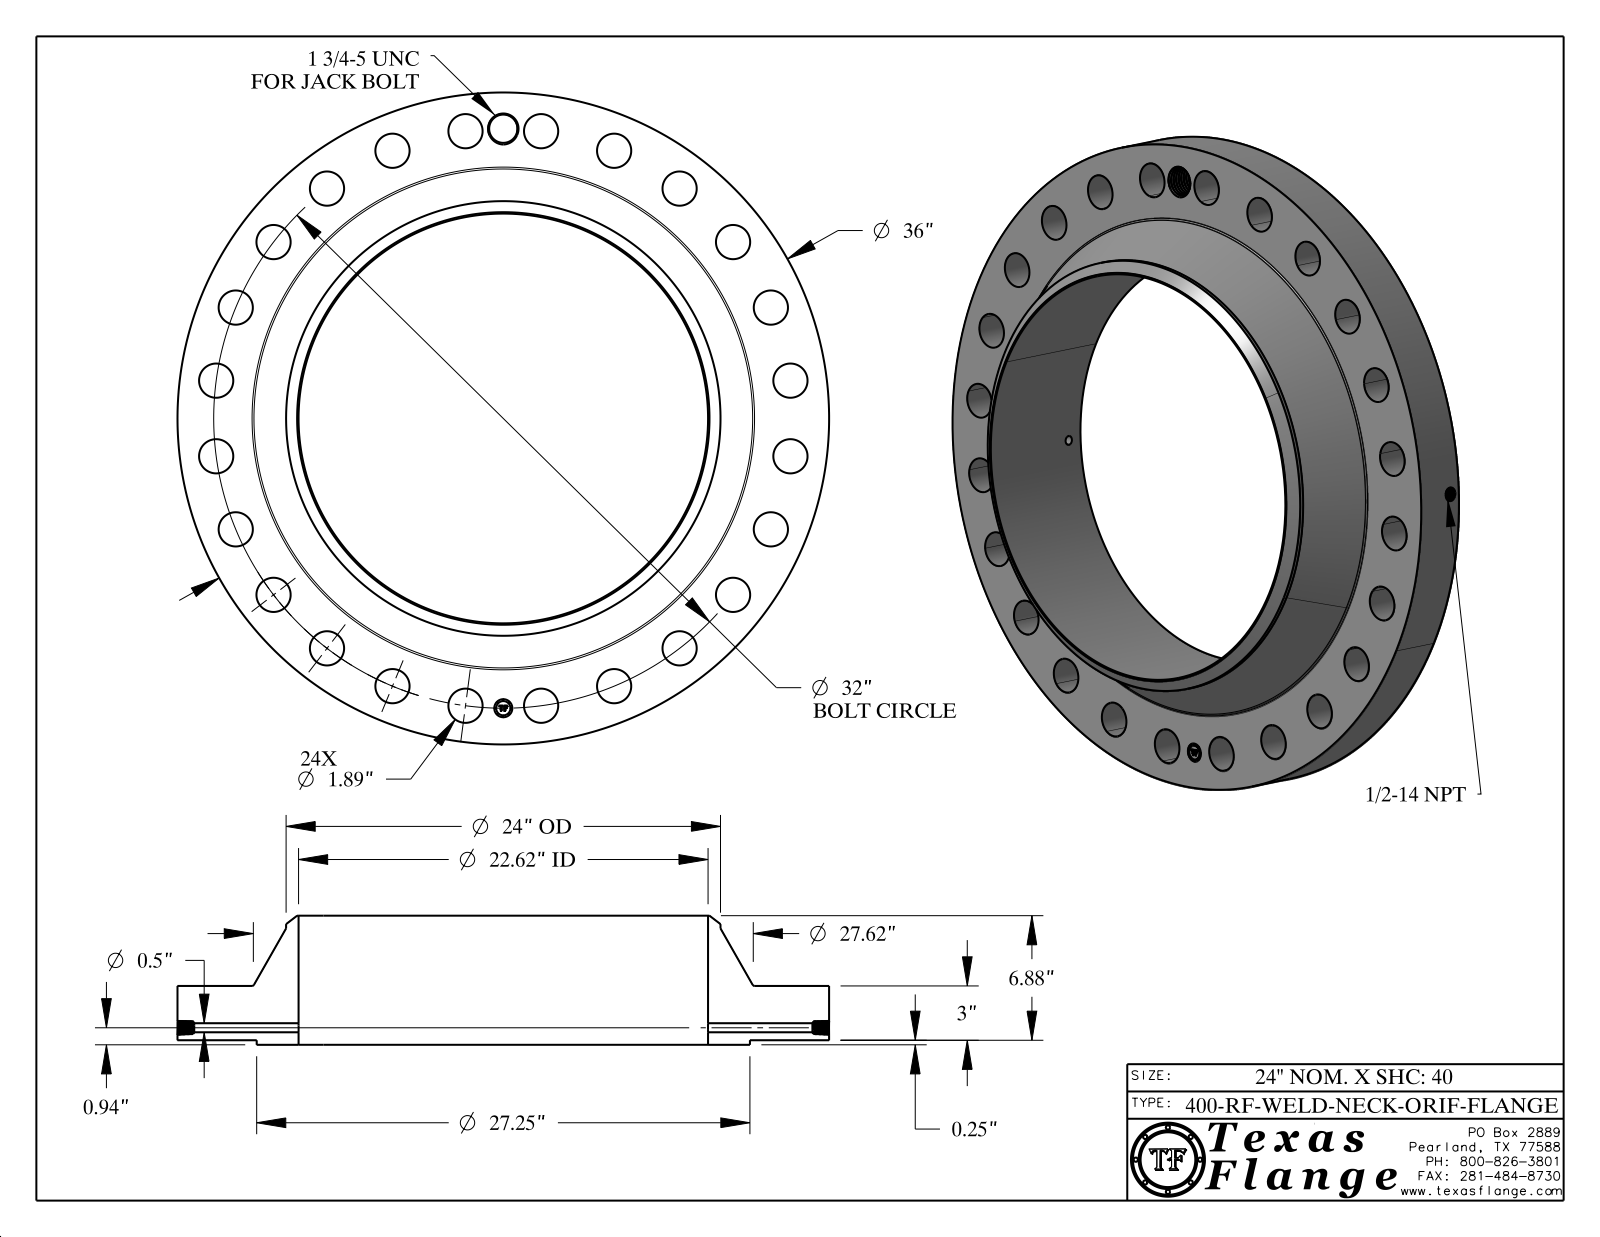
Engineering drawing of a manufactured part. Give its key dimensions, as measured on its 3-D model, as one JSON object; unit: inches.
{"part_name": "400-RF-WELD-NECK", "step_written_by": "CATIA V5 STEP AP214 (AUTOMOTIVE_DESIGN)", "units": "inches", "bodies": {"solids": 1, "faces": 801, "planar": 369, "cylindrical": 126, "other": 306}, "overall_size": [36, 36, 7.13], "volume_in3": 2094, "surface_area_in2": 2612, "round_holes": [[1.89, 24], [0.5, 1], [0.672, 1], [1, 1], [1.563, 1], [22.624, 1]], "round_bosses_or_shafts": [[0.061, 8], [36, 1], [27.25, 1], [24, 1], [0.788, 1]], "face_to_face_distances": [3, 0.25, 3.25, 7.13, 6.88, 3.88, 3.235, 2.985, 0.015, 3.895], "hole_center_spacings": [16, 27.713, 30.909, 4.177, 19.48, 31.726, 8.282, 12.246]}
